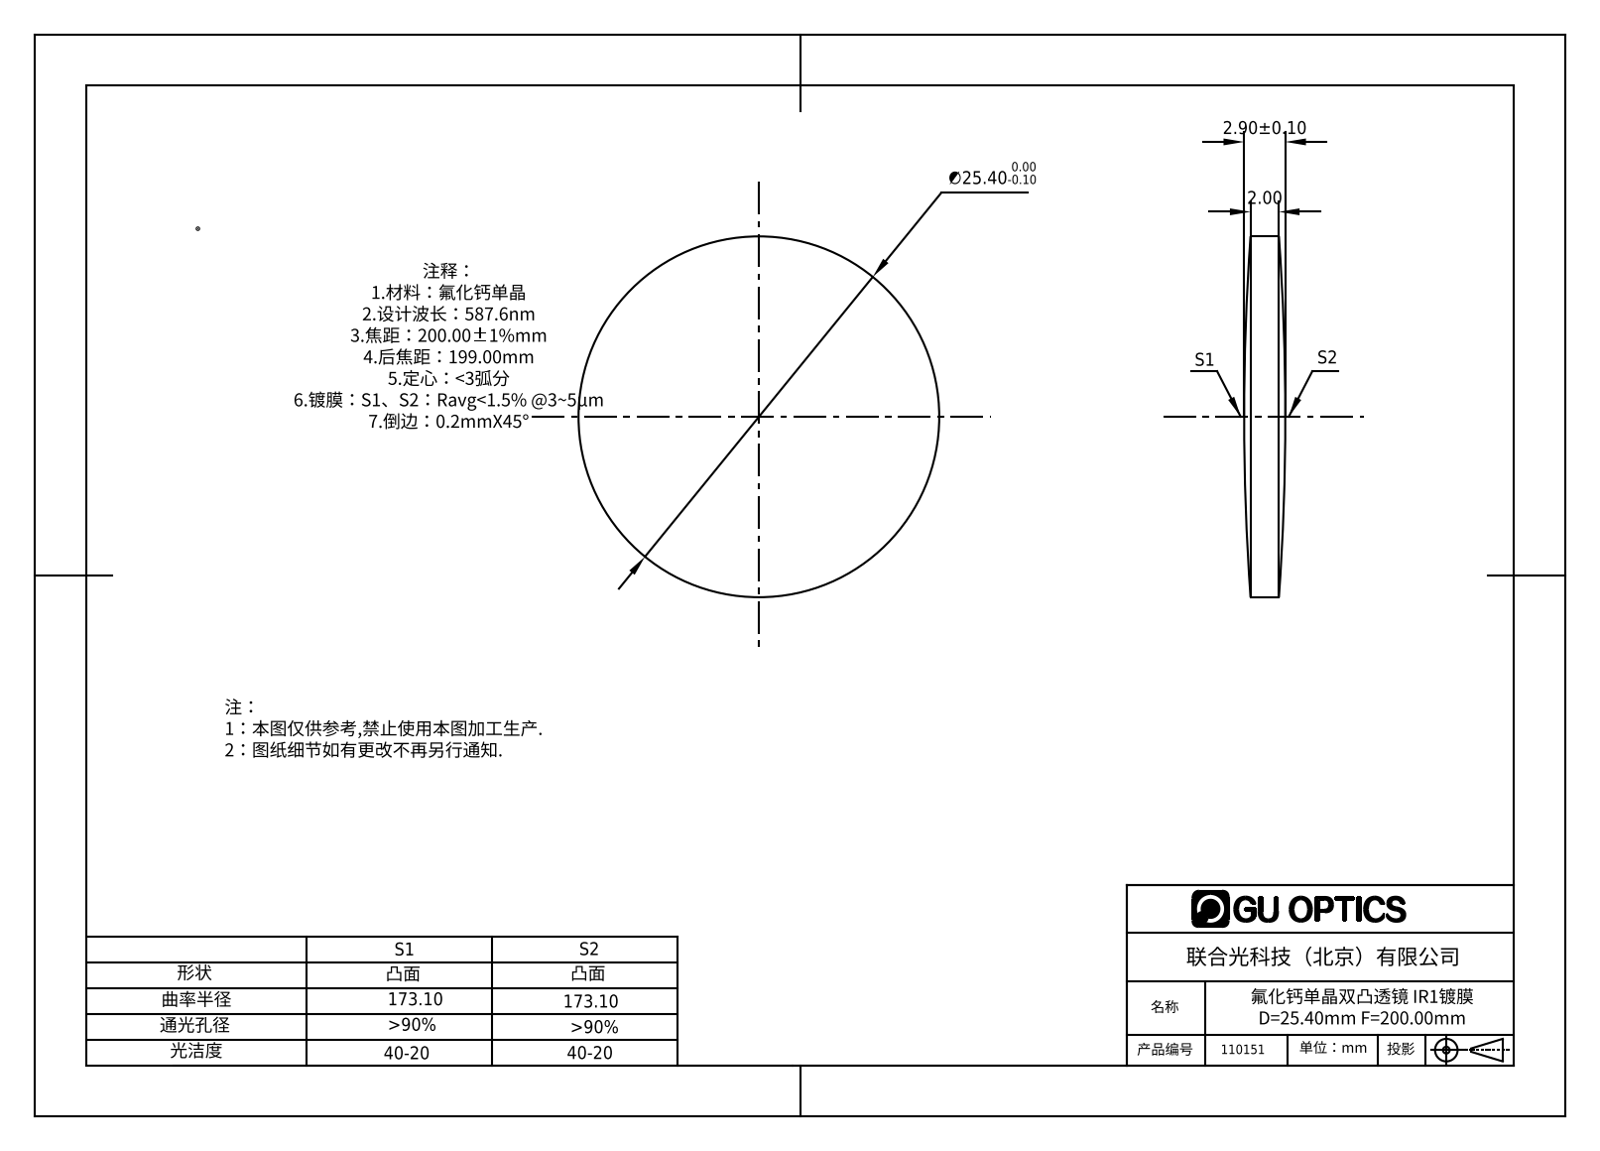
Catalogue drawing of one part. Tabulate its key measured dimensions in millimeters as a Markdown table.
| quantity | value |
| --- | --- |
| part name | 110143 |
| STEP written by | SolidWorks 2016 (CONFIG_CONTROL_DESIGN) |
| units | millimeters |
| bodies | 1 solid, 6 faces (0 planar, 2 cylindrical, 4 other) |
| overall size | 25.4 × 25.4 × 2.9 |
| volume | 1 241 mm³ |
| surface area | 1 174 mm² |
| round bosses / shafts (diameter × count) | 25.4 × 1 |
